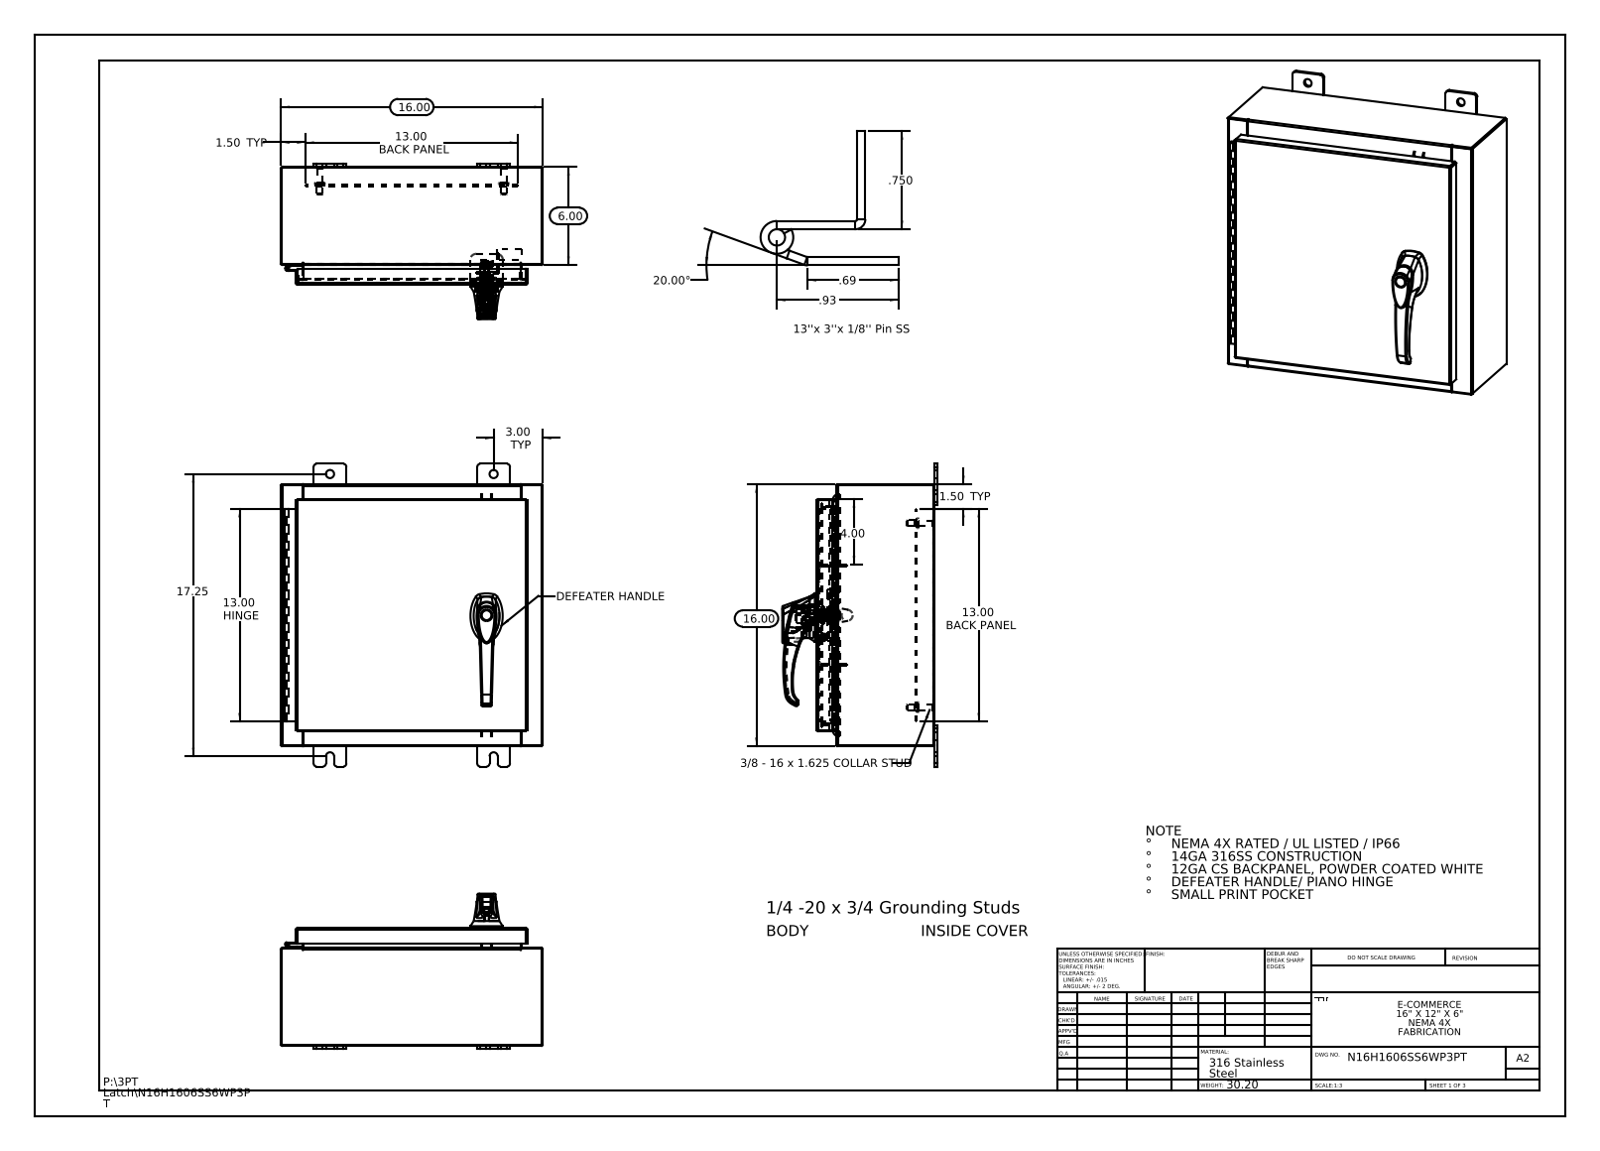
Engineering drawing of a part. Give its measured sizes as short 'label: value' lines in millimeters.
name: NMP-SS-RODGUIDES; N16H1606SS6WP3PT Bottom; N16H1606SS6WP3PT Defeater Handle Rod; 00005309_G26103101 (+8 more)
written by: SolidWorks 2013 (CONFIG_CONTROL_DESIGN)
unit: mm
bodies: 31 solids, 2204 faces (757 planar, 793 cylindrical, 654 other)
size: 469.9 × 406.4 × 241.2
volume: 1 781 000 mm³; area: 1 717 000 mm²
holes: 8× ⌀12.7, 4× ⌀6.4, 3× ⌀3.5, 3× ⌀4.1, 2× ⌀2, 2× ⌀5.2, 2× ⌀8, 2× ⌀11.1, 1× ⌀3.2, 1× ⌀3.2, 1× ⌀5, 1× ⌀7
bosses: 4× ⌀15.9, 4× ⌀9.5, 4× ⌀8.4, 1× ⌀30, 1× ⌀19, 1× ⌀17.3, 1× ⌀16.8, 1× ⌀16.2
rounds: 37× R3, 33× R0.2, 24× R4.8, 20× R0.3, 18× R2.2, 15× R1, 12× R0.7, 6× R0.2
face distances: 1.9, 181, 404.5, 179.1, 182.9, 402.6, 406.4, 25.4, 2.6, 27.3
hole spacings: 94.2, 7.5, 15.9, 21.4, 31.8, 33.4, 33.5, 37.7
